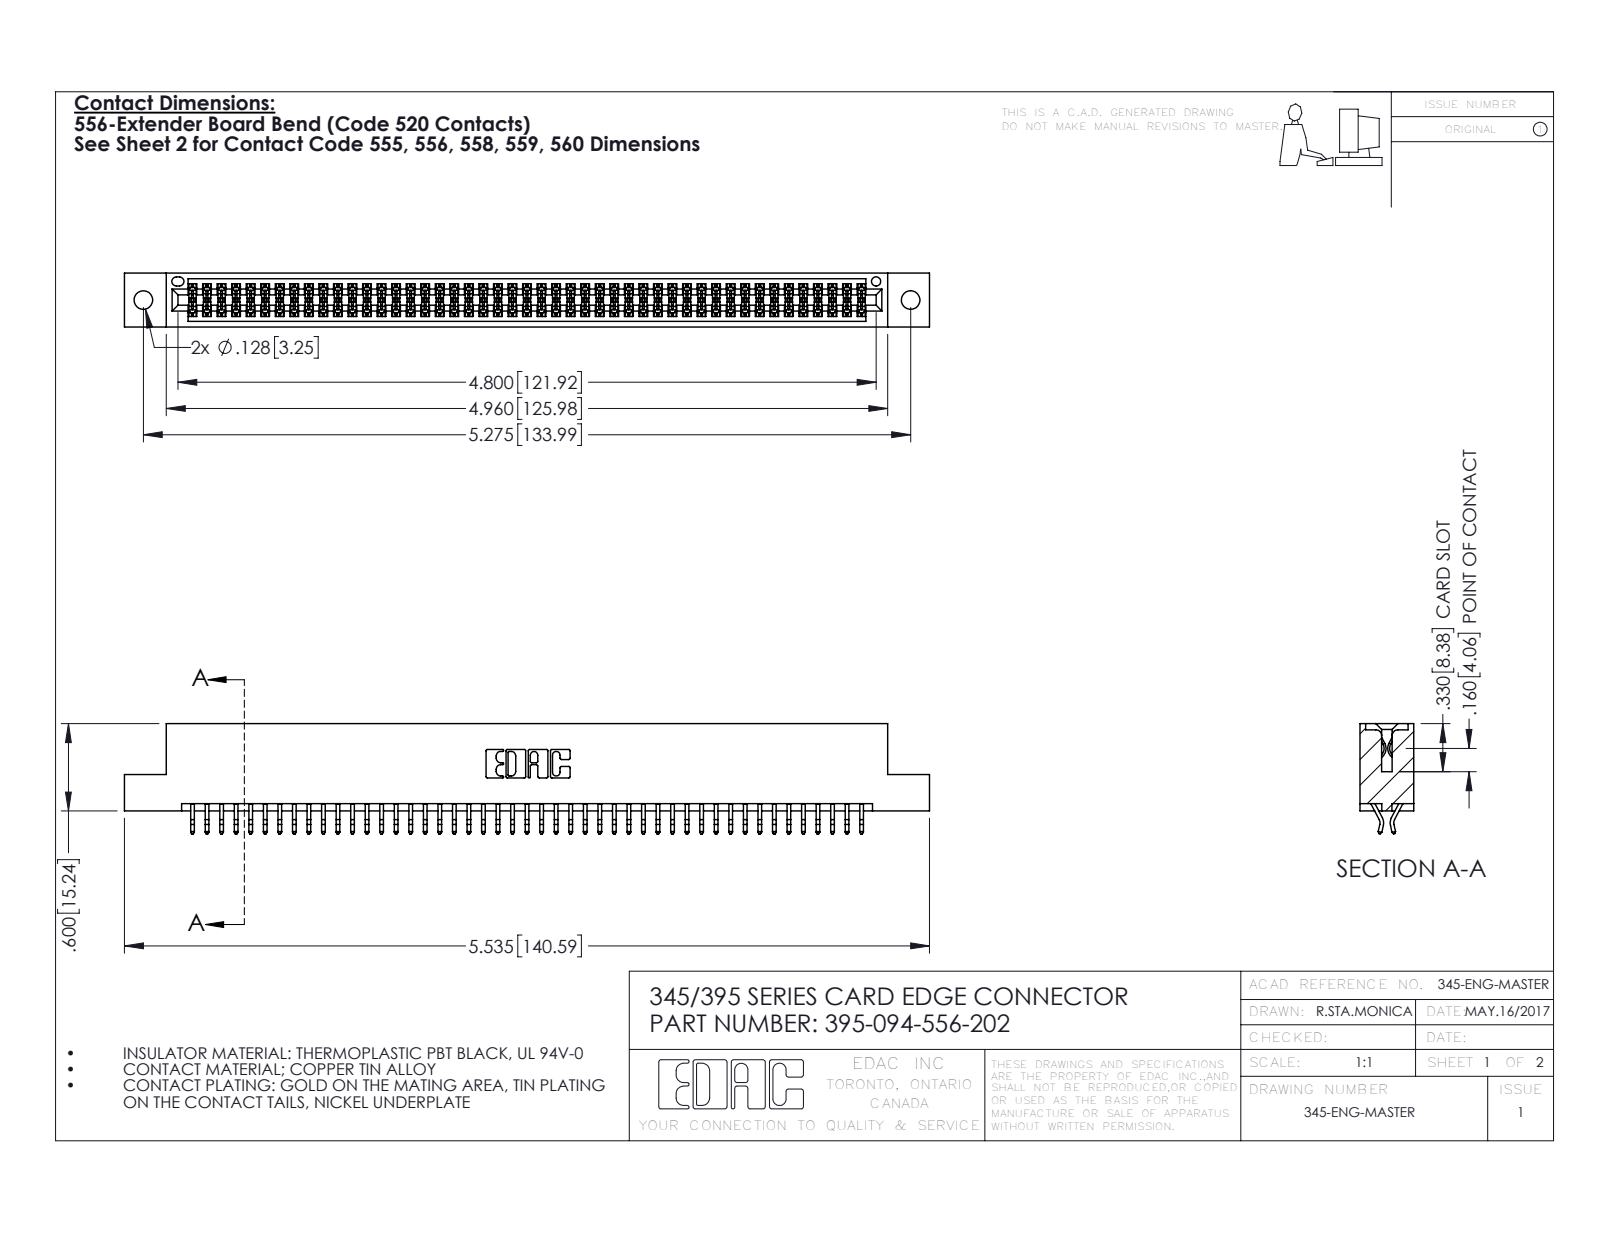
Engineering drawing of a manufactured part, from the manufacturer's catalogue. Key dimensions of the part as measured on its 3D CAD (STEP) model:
Part name (STEP PRODUCT): 345-292-001_556 Tail; 345 Part_Flush Mounting Lugs - 0.128 Dia; 395-094-556-202
STEP written by: SolidWorks 2016 (CONFIG_CONTROL_DESIGN)
Units: inches
Bodies: 95 solids, 5390 faces (3558 planar, 1832 cylindrical, 0 other)
Overall size (bounding box): 5.535 × 0.757 × 0.37
Volume: 0.834 in³ · Surface area: 30.9 in²
Round holes (diameter × count): ⌀0.128 ×2, ⌀0.064 ×1
Partial cylindrical surfaces — rounded edges, fillets, slot ends (radius × count): R0.006 ×141, R0.01 ×22, R0.007 ×6, R0.031 ×6, R0.026 ×3, R0.01 ×2, R0.014 ×2, R0.019 ×2
Main face-to-face distances: 0.298, 0.072, 0.2, 0.37, 0.025, 0.098, 0.272, 0.225, 0.175, 0.149
Hole centre spacings: 0.27, 5.039, 5.275
